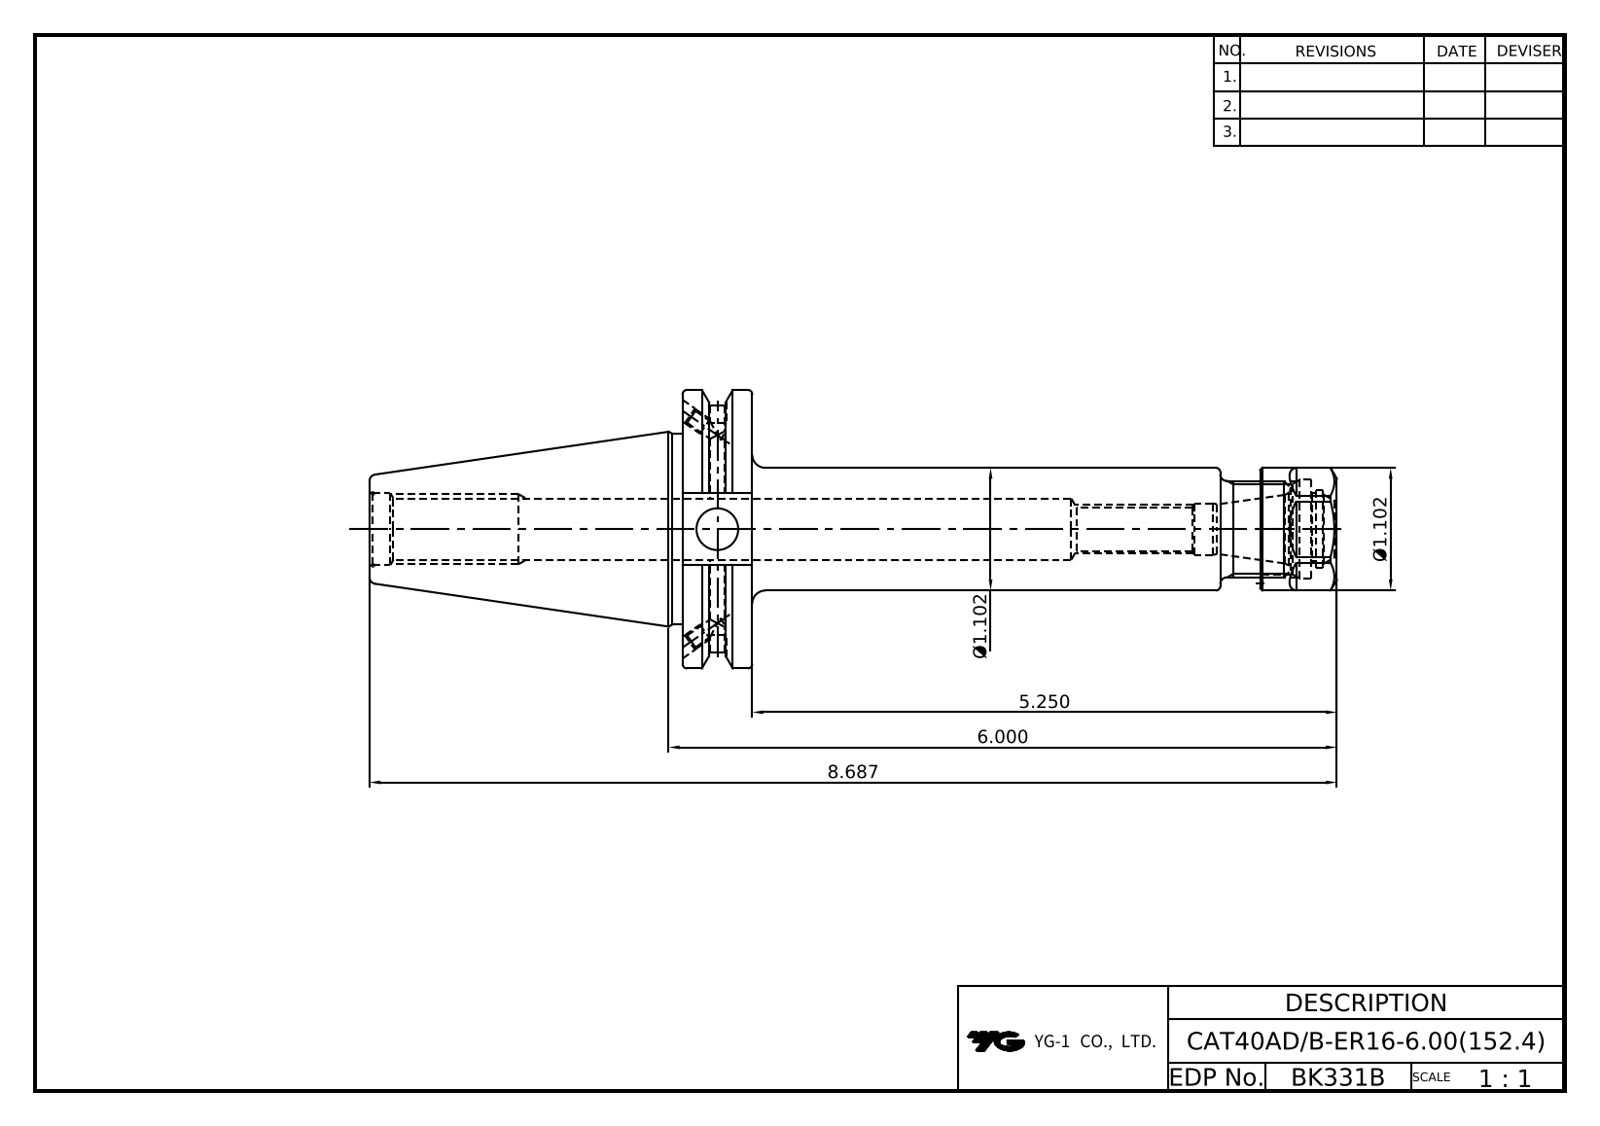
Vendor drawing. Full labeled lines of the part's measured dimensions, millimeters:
Part name (STEP PRODUCT): LO-CAT40ADB-ER16-6.00; ER16NUT
STEP written by: Autodesk Inventor 2025 (AUTOMOTIVE_DESIGN)
Units: millimetres
Bodies: 2 solids, 123 faces (56 planar, 37 cylindrical, 30 other)
Overall size (bounding box): 220.65 × 63.5 × 61.09
Volume: 161 778 mm³ · Surface area: 39 843 mm²
Round holes (diameter × count): ⌀3.24 ×4, ⌀4 ×2, ⌀4.2 ×2, ⌀1 ×1, ⌀9.4 ×1, ⌀9.53 ×1, ⌀11.8 ×1, ⌀12.8 ×1, ⌀13.39 ×1, ⌀16.3 ×1, ⌀17.7 ×1, ⌀20.6 ×1
Round bosses / shafts (diameter × count): ⌀63.5 ×1, ⌀43.6 ×1, ⌀28 ×1, ⌀22 ×1
Partial cylindrical surfaces — rounded edges, fillets, slot ends (radius × count): R7.7 ×2, R28.15 ×1
Main face-to-face distances: 15.88, 25, 149.23, 133.35, 143.43, 127.55, 5.8, 47.6, 131.73, 115.85
Hole centre spacings: 12
